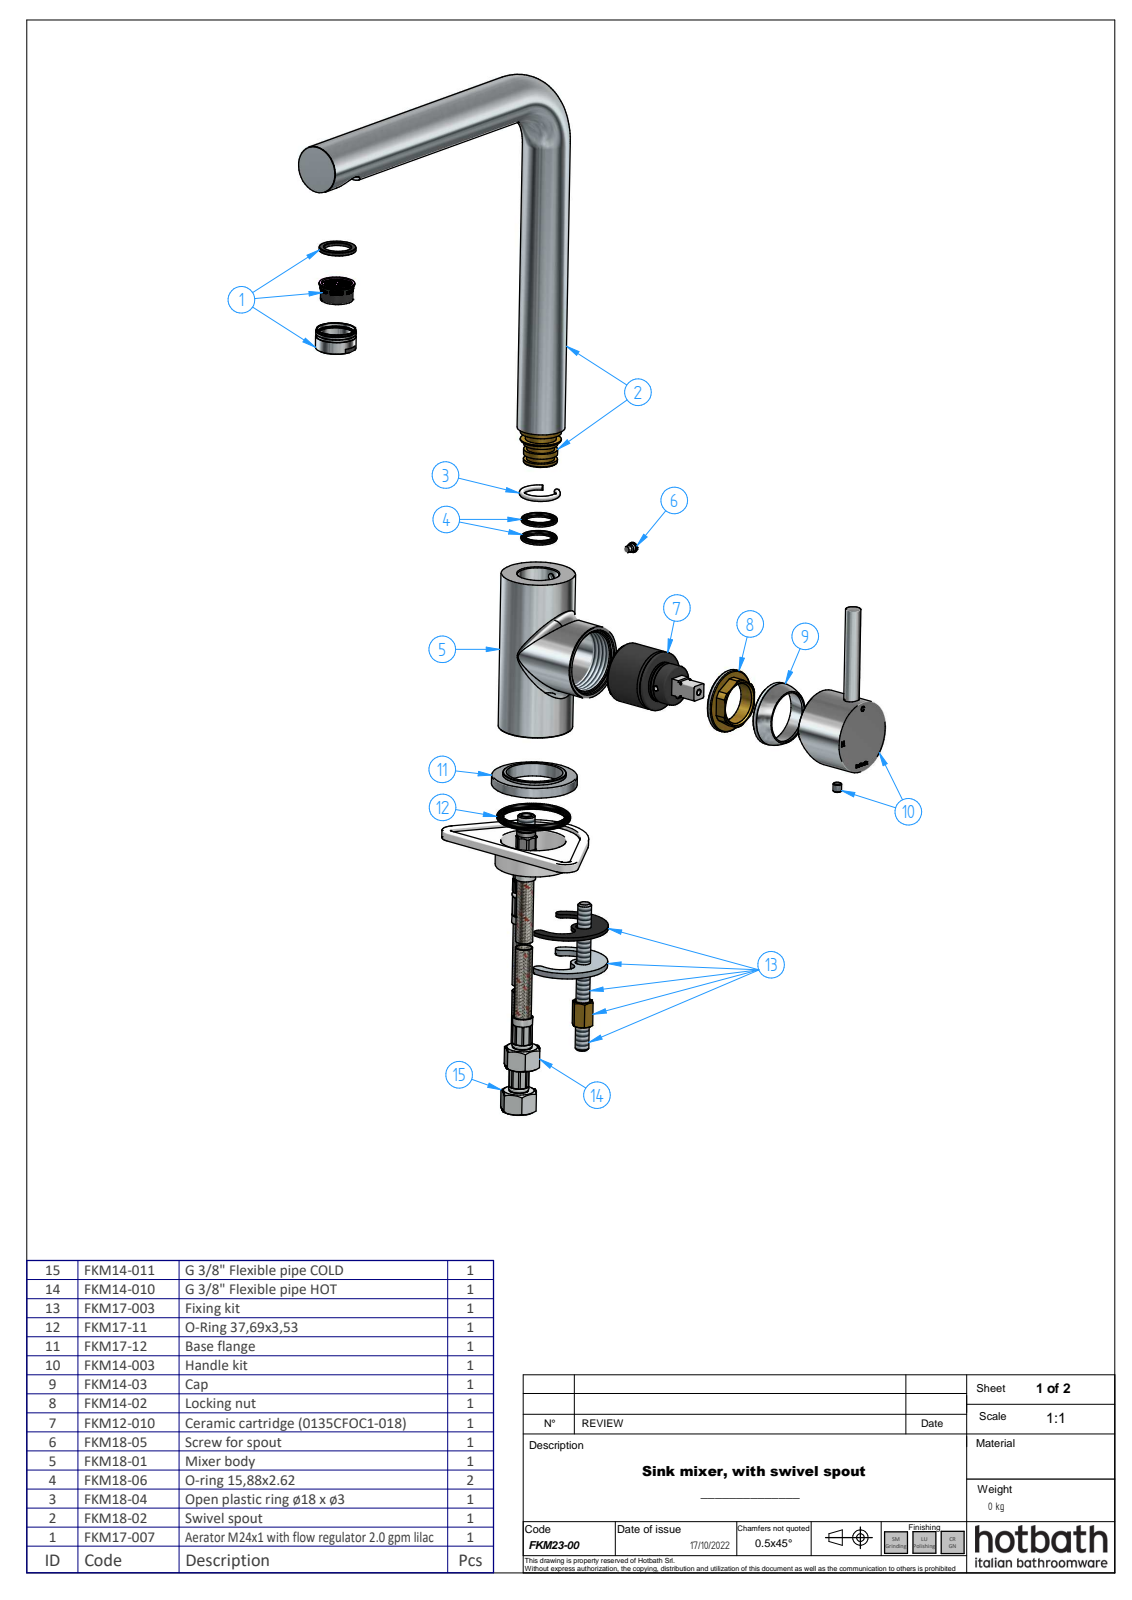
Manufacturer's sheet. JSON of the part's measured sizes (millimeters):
{"part_name": "FKM23-00; FKM17-007_oa_0; cartuccia lilac_oa_1; p5 (+8 more)", "step_written_by": "ST-DEVELOPER v16.7 (AUTOMOTIVE_DESIGN)", "units": "millimeters", "bodies": {"solids": 8, "faces": 822, "planar": 196, "cylindrical": 455, "other": 171}, "overall_size": [324, 235, 100.55], "volume_mm3": 203628, "surface_area_mm2": 118324, "round_holes": [[8.92, 2], [11, 2], [24, 2], [3.24, 1], [4.13, 1], [6.5, 1], [6.65, 1], [16.7, 1], [16.8, 1], [18.15, 1], [19.15, 1], [20, 1]], "round_bosses_or_shafts": [[0.24, 26], [43, 2], [37, 2], [28, 2], [50, 1], [43.5, 1], [36.7, 1], [23.7, 1]], "partial_cylinders_radius": [[0.3, 32], [0.5, 27], [1, 8], [0.49, 1], [3, 1]], "face_to_face_distances": [2, 94, 68.3, 19, 75, 3, 65.3, 6, 25, 4], "hole_center_spacings": [9.43, 15.27, 8, 15.99, 52.04, 56.5, 57.58, 66.74]}
